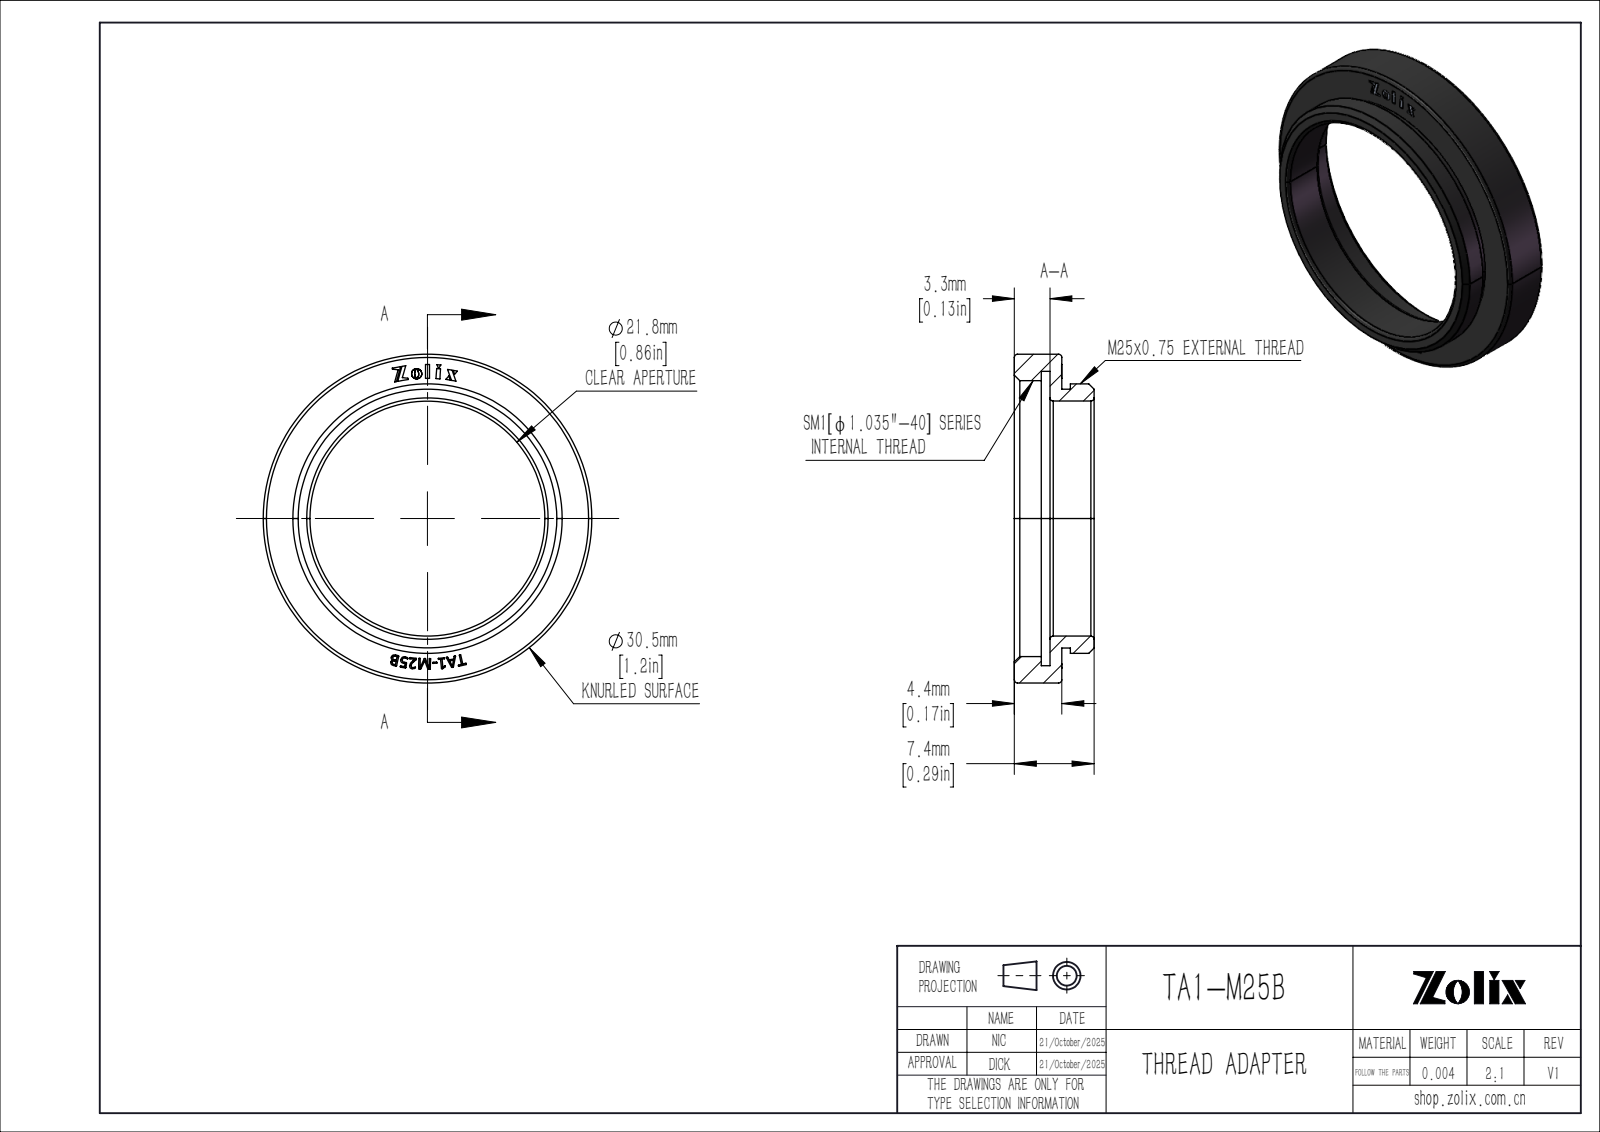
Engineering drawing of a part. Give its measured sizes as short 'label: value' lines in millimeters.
name: TA1-M25B
written by: SolidWorks 2020 (CONFIG_CONTROL_DESIGN)
unit: mm
bodies: 1 solid, 321 faces (221 planar, 12 cylindrical, 88 other)
size: 30.5 × 30.5 × 7.4
volume: 1 345 mm³; area: 2 050 mm²
holes: 1× ⌀21.8, 1× ⌀25.6, 1× ⌀27.3
bosses: 1× ⌀30.5, 1× ⌀25, 1× ⌀24
face distances: 1.1, 4.4, 3.3, 0.8, 1.9, 2.5, 3, 4.1, 4.9, 7.4
